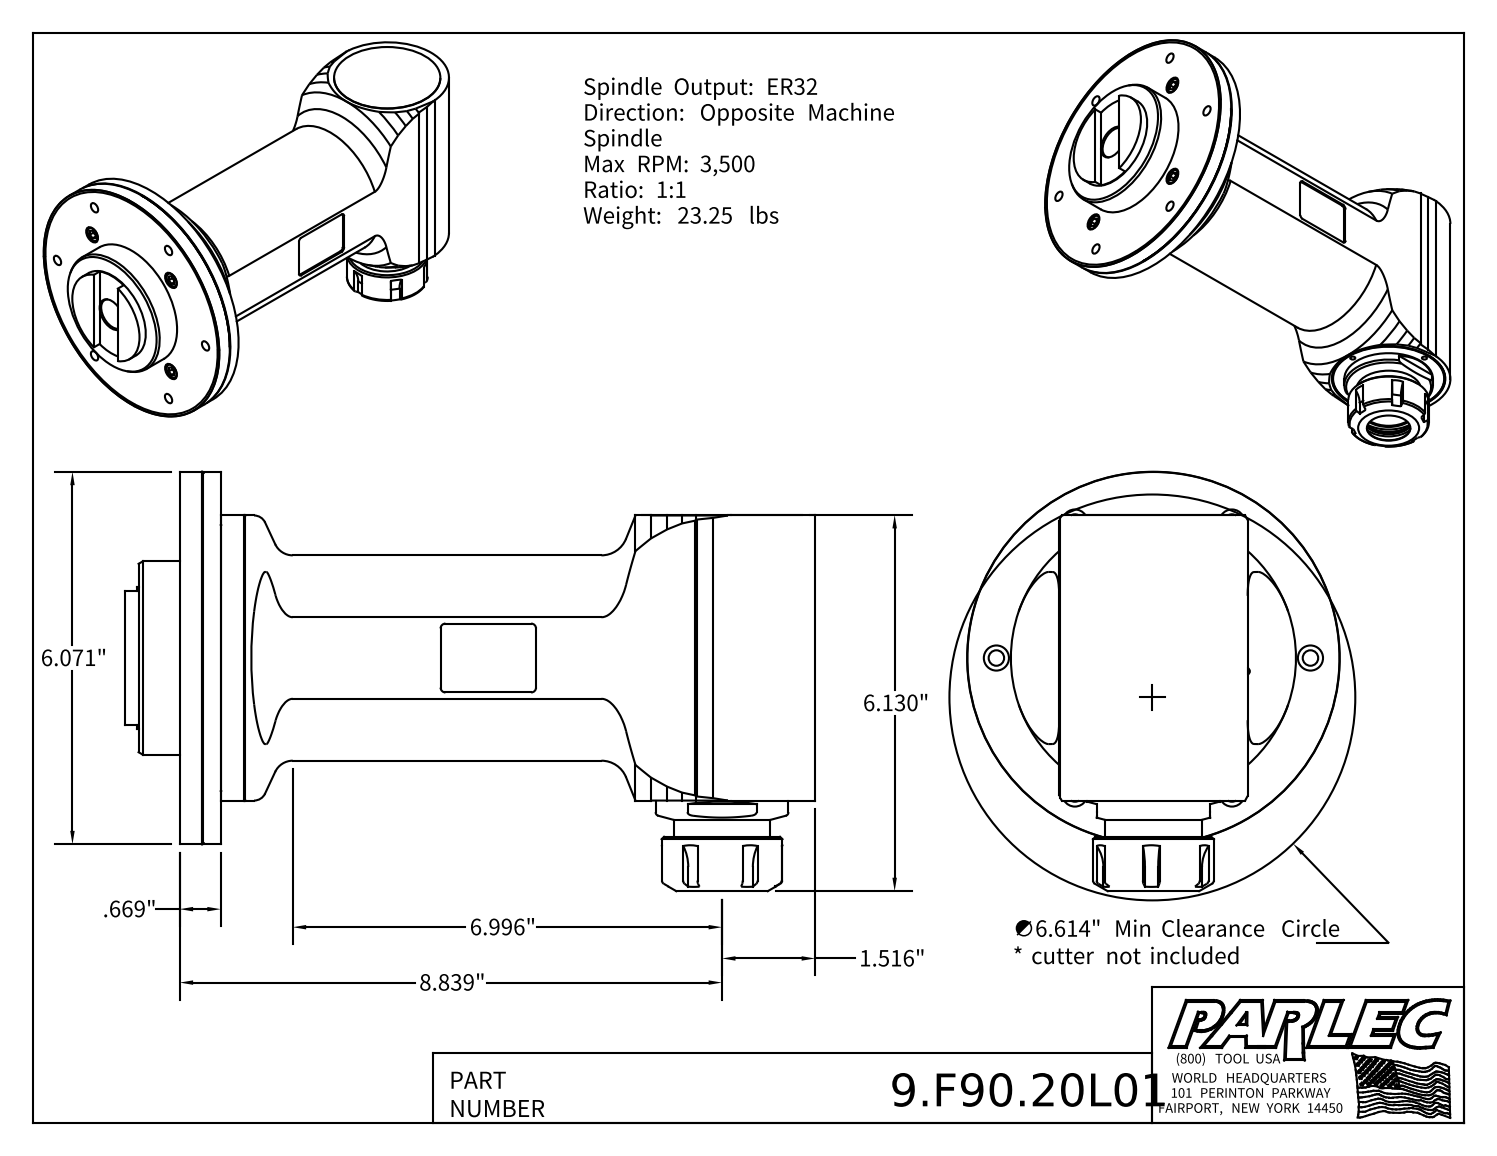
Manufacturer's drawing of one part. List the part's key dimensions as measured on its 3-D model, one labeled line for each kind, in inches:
Part name (STEP PRODUCT): 9.F90.20L01; 9_F90_20L01
STEP written by: Autodesk Inventor 2022 (AUTOMOTIVE_DESIGN)
Units: inches
Bodies: 3 solids, 288 faces (131 planar, 81 cylindrical, 76 other)
Overall size (bounding box): 11.24 × 6.835 × 6.071
Volume: 127.9 in³ · Surface area: 275 in²
Round holes (diameter × count): ⌀0.409 ×10, ⌀0.252 ×6, ⌀0.126 ×4, ⌀0.492 ×1, ⌀0.787 ×1, ⌀0.945 ×1, ⌀1.063 ×1, ⌀1.161 ×1, ⌀1.409 ×1, ⌀1.516 ×1, ⌀1.598 ×1, ⌀3.15 ×1
Round bosses / shafts (diameter × count): ⌀0.394 ×4, ⌀0.236 ×4, ⌀0.098 ×2, ⌀6.071 ×1, ⌀6.063 ×1, ⌀4.646 ×1, ⌀2.756 ×1, ⌀2.598 ×1
Partial cylindrical surfaces — rounded edges, fillets, slot ends (radius × count): R0.079 ×12, R0.591 ×6, R0.157 ×2, R1.496 ×1, R1.673 ×1
Main face-to-face distances: 0.669, 3.071, 0.02, 1.339, 0.886, 0.217, 4.654, 1.555, 0.677, 0.039
Hole centre spacings: 2.559, 0.857, 1.24, 1.754, 1.929, 2.559, 2.778, 3.581
